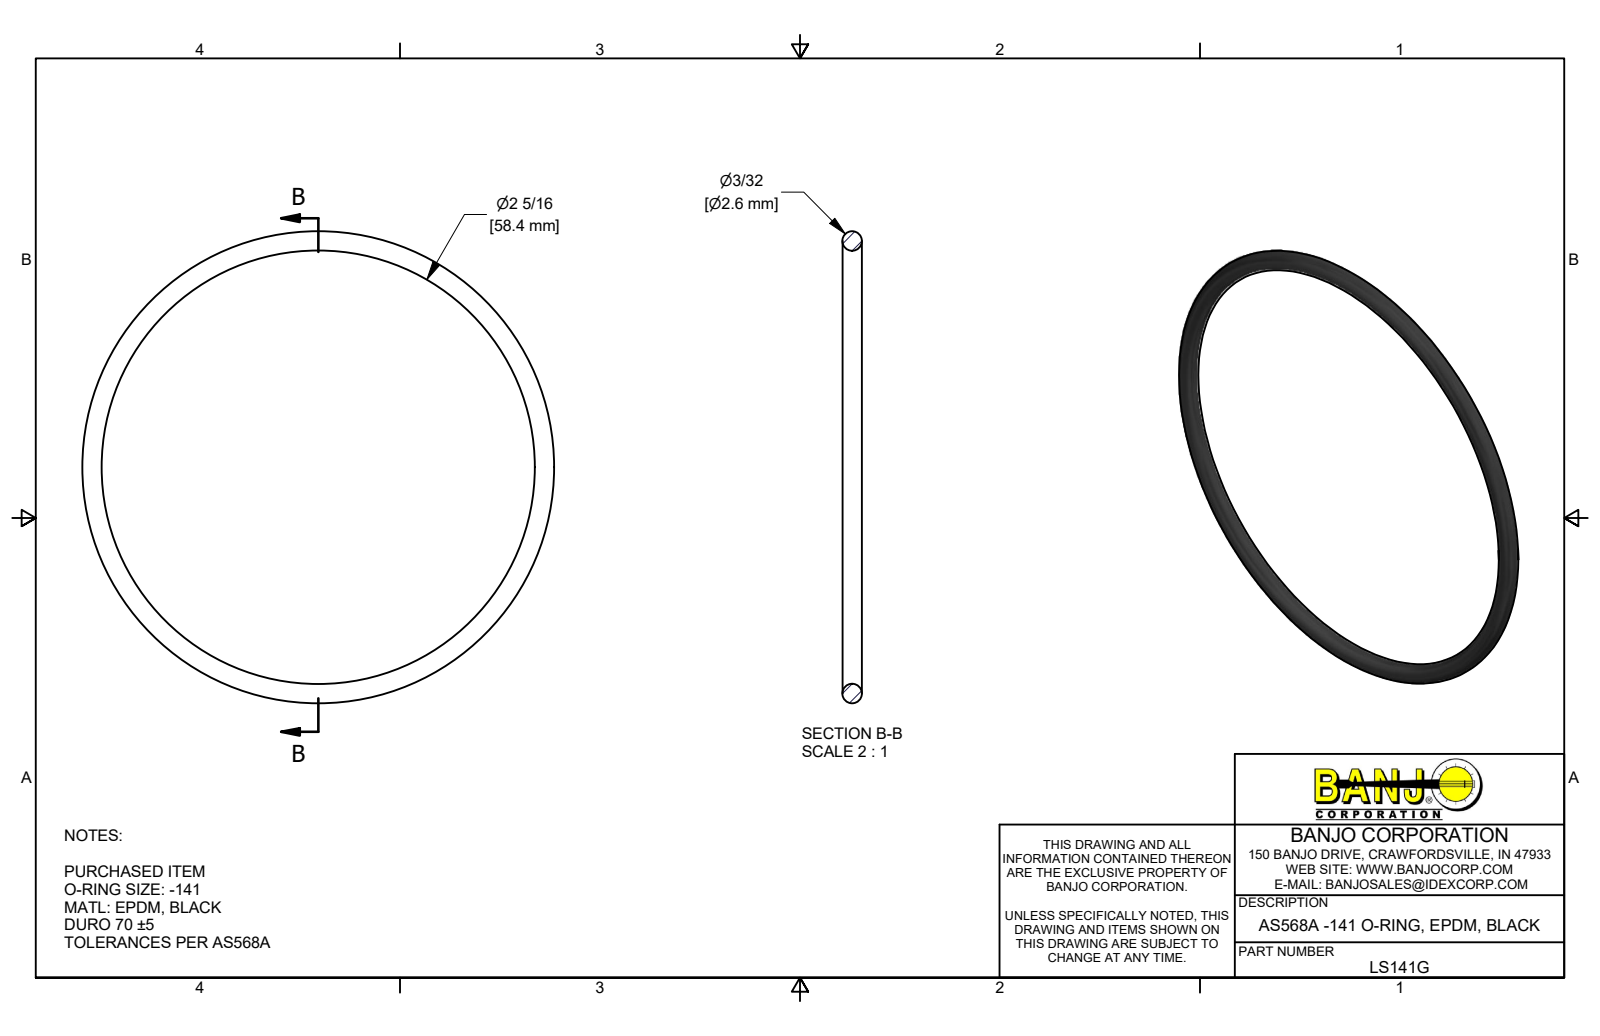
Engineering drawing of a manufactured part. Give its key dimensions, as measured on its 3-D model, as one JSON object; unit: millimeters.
{"part_name": "LS141G", "step_written_by": "Autodesk Inventor 2019 (AUTOMOTIVE_DESIGN)", "units": "millimeters", "bodies": {"solids": 1, "faces": 1, "planar": 0, "cylindrical": 0, "other": 1}, "overall_size": [63.7, 63.7, 2.6], "volume_mm3": 1000, "surface_area_mm2": 1576}
